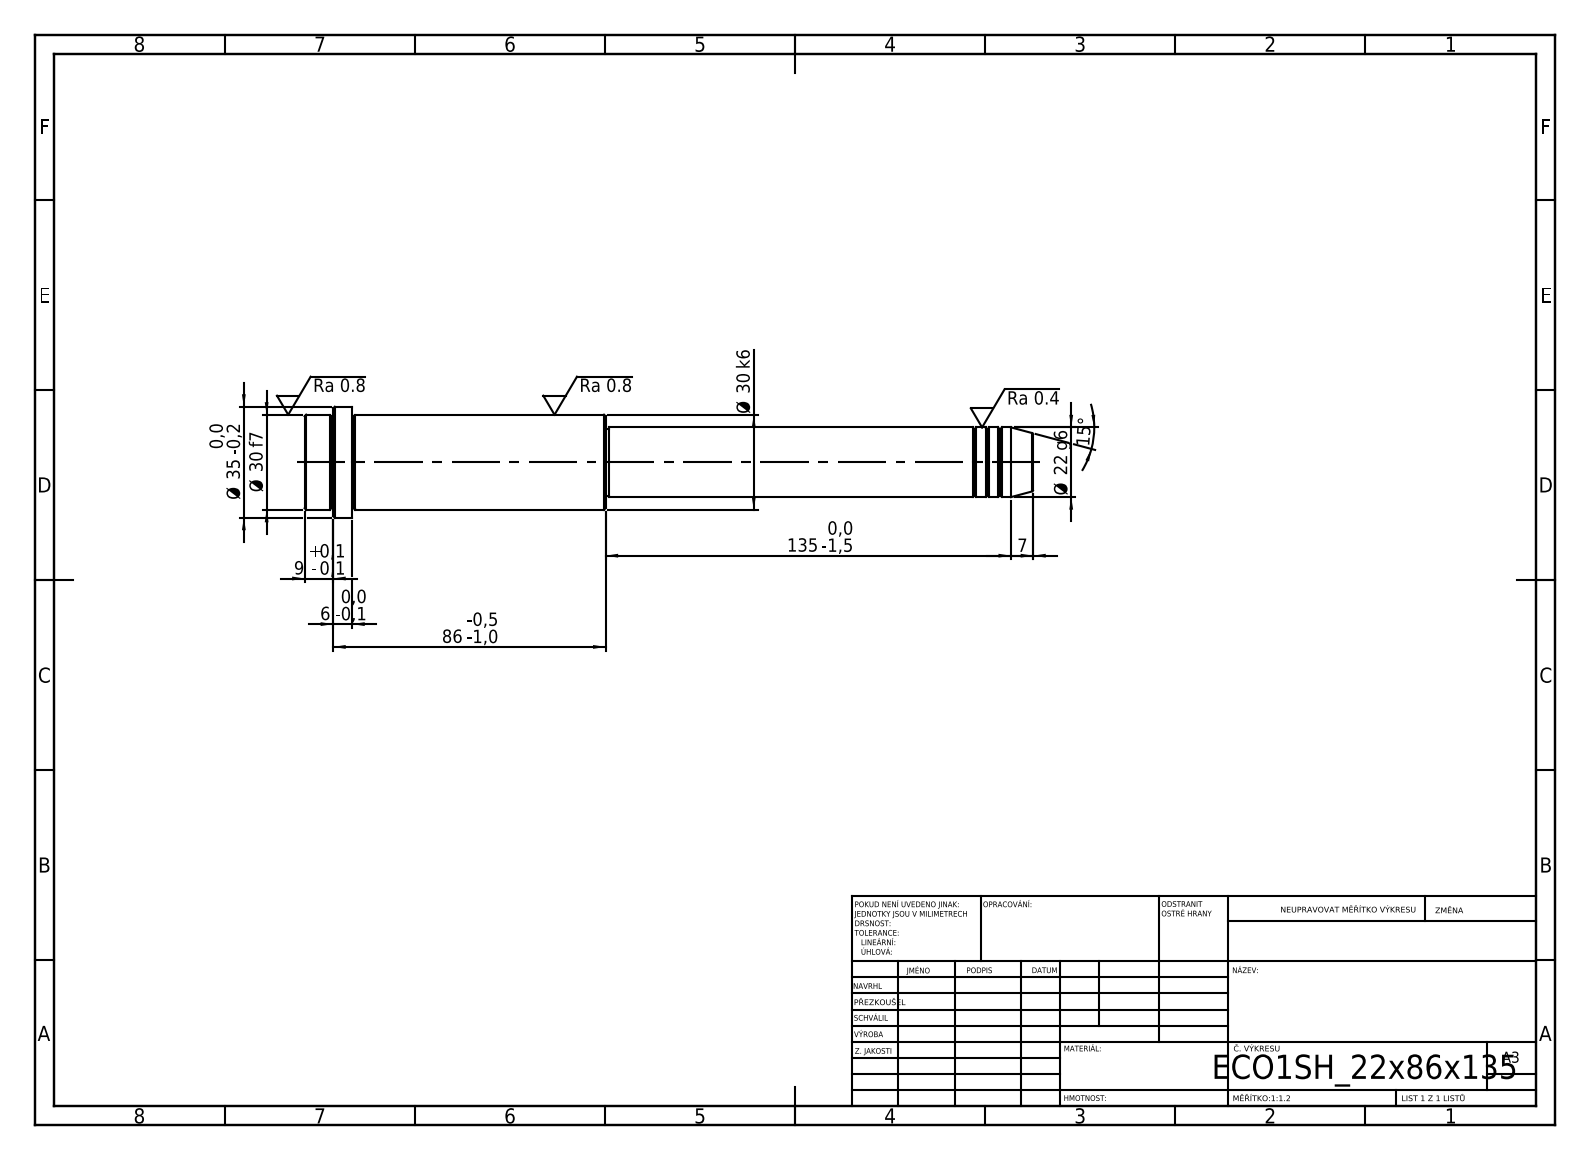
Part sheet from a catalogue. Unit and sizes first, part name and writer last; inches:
Units: inches
Overall size (bounding box): 9.055 × 1.378 × 1.378
Round bosses / shafts (diameter × count): ⌀1.378 ×1, ⌀1.181 ×1, ⌀0.866 ×1, ⌀0.827 ×1
Main face-to-face distances: 3.74, 3.15, 0.591, 5.315, 8.465, 9.055, 8.701, 3.386, 0.236, 0.354
Volume: 7.283 in³ · Surface area: 31.52 in²
Bodies: 1 solid, 52 faces (6 planar, 16 cylindrical, 30 other)
STEP written by: SolidWorks 2019 (CONFIG_CONTROL_DESIGN)
